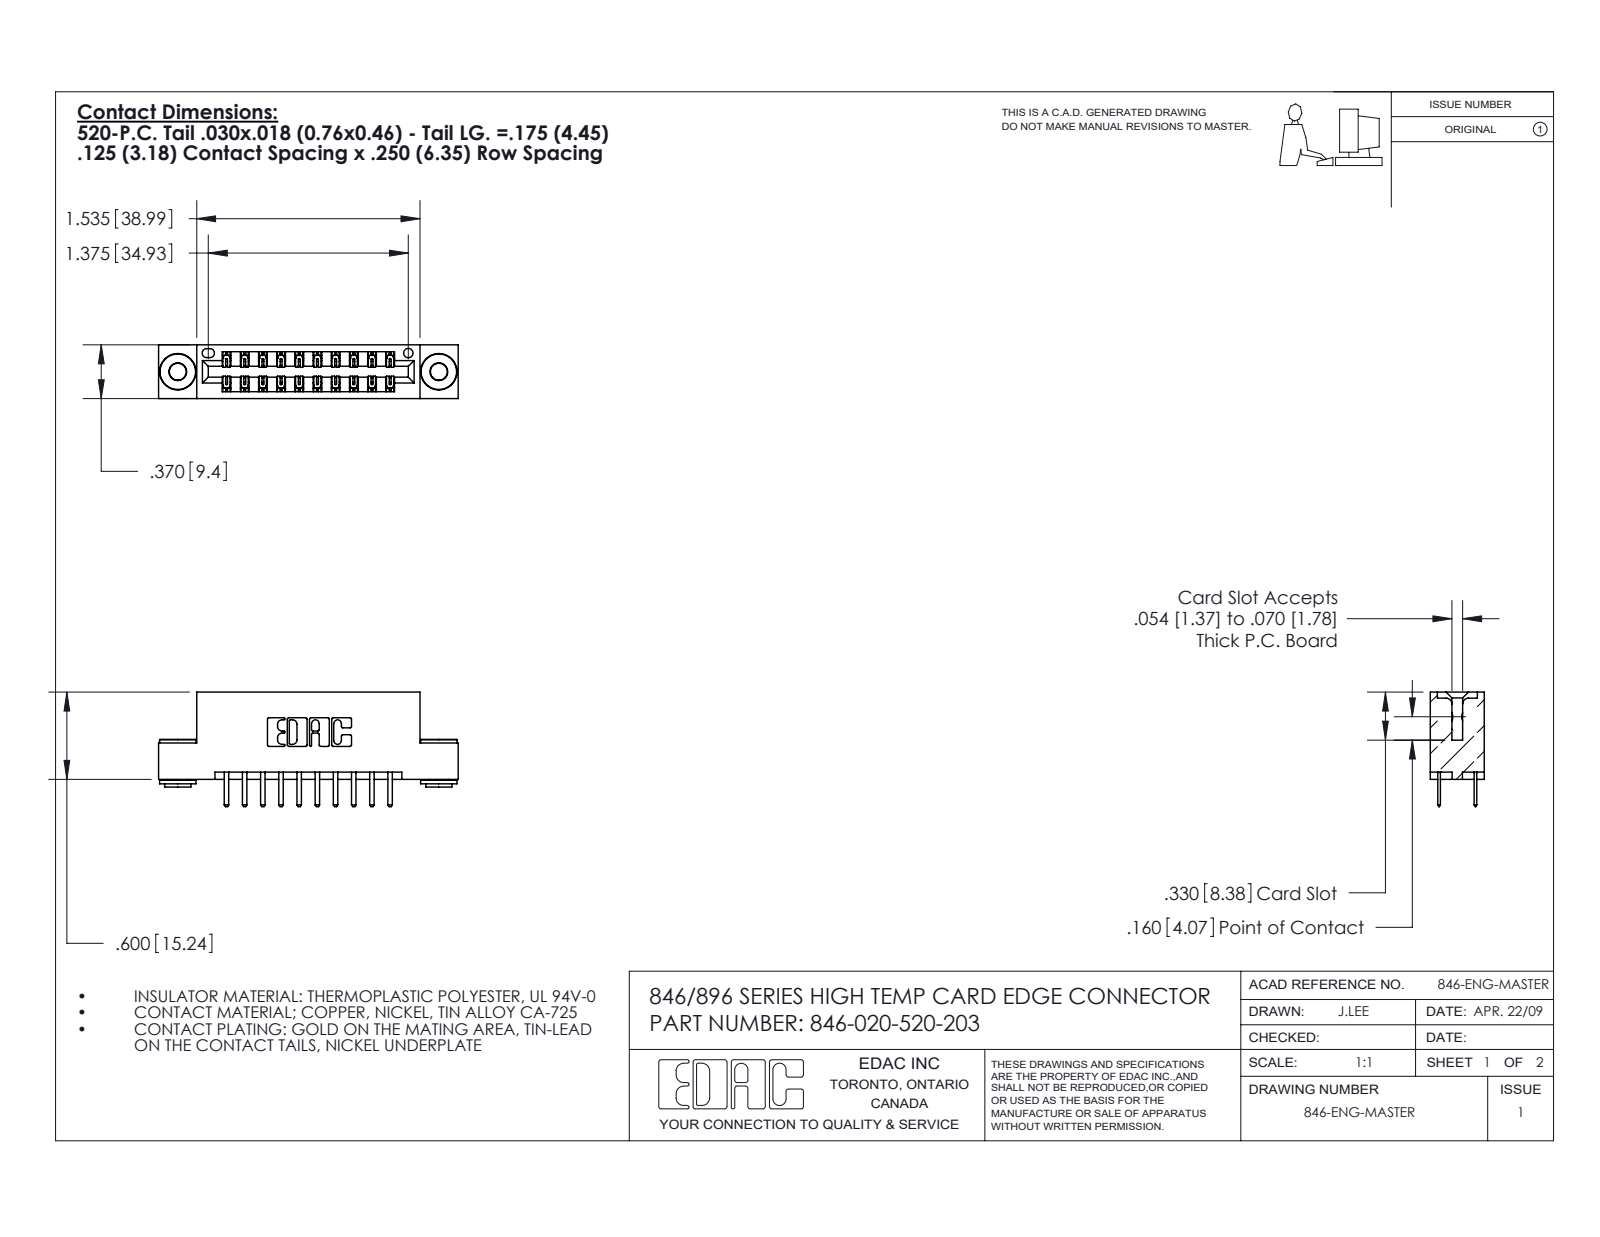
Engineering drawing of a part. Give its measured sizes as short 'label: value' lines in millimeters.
name: 346-020-520-203; 346 Part_Flush Mounting Lugs - 0.156 Dia-TH; 345-292-001_345-293-120; 345-250-002_345-250-002-102
written by: SolidWorks 2016 (CONFIG_CONTROL_DESIGN)
unit: mm
bodies: 18 solids, 1030 faces (666 planar, 356 cylindrical, 8 other)
size: 52.3 × 20 × 9.4
volume: 4 820 mm³; area: 6 064 mm²
holes: 2× ⌀2.9, 2× ⌀4, 1× ⌀1.6
bosses: 2× ⌀6.4, 2× ⌀4.6, 2× ⌀3.5
rounds: 25× R0.2, 24× R0.3, 22× R0.3, 6× R0.2, 6× R0.8, 3× R0.7, 2× R0.4, 2× R0.6
face distances: 6.4, 9.4, 1.2, 8.2, 3.8, 0.6, 5.6, 2.5, 4.4, 1.8
hole spacings: 6.2, 40.4, 45.6
